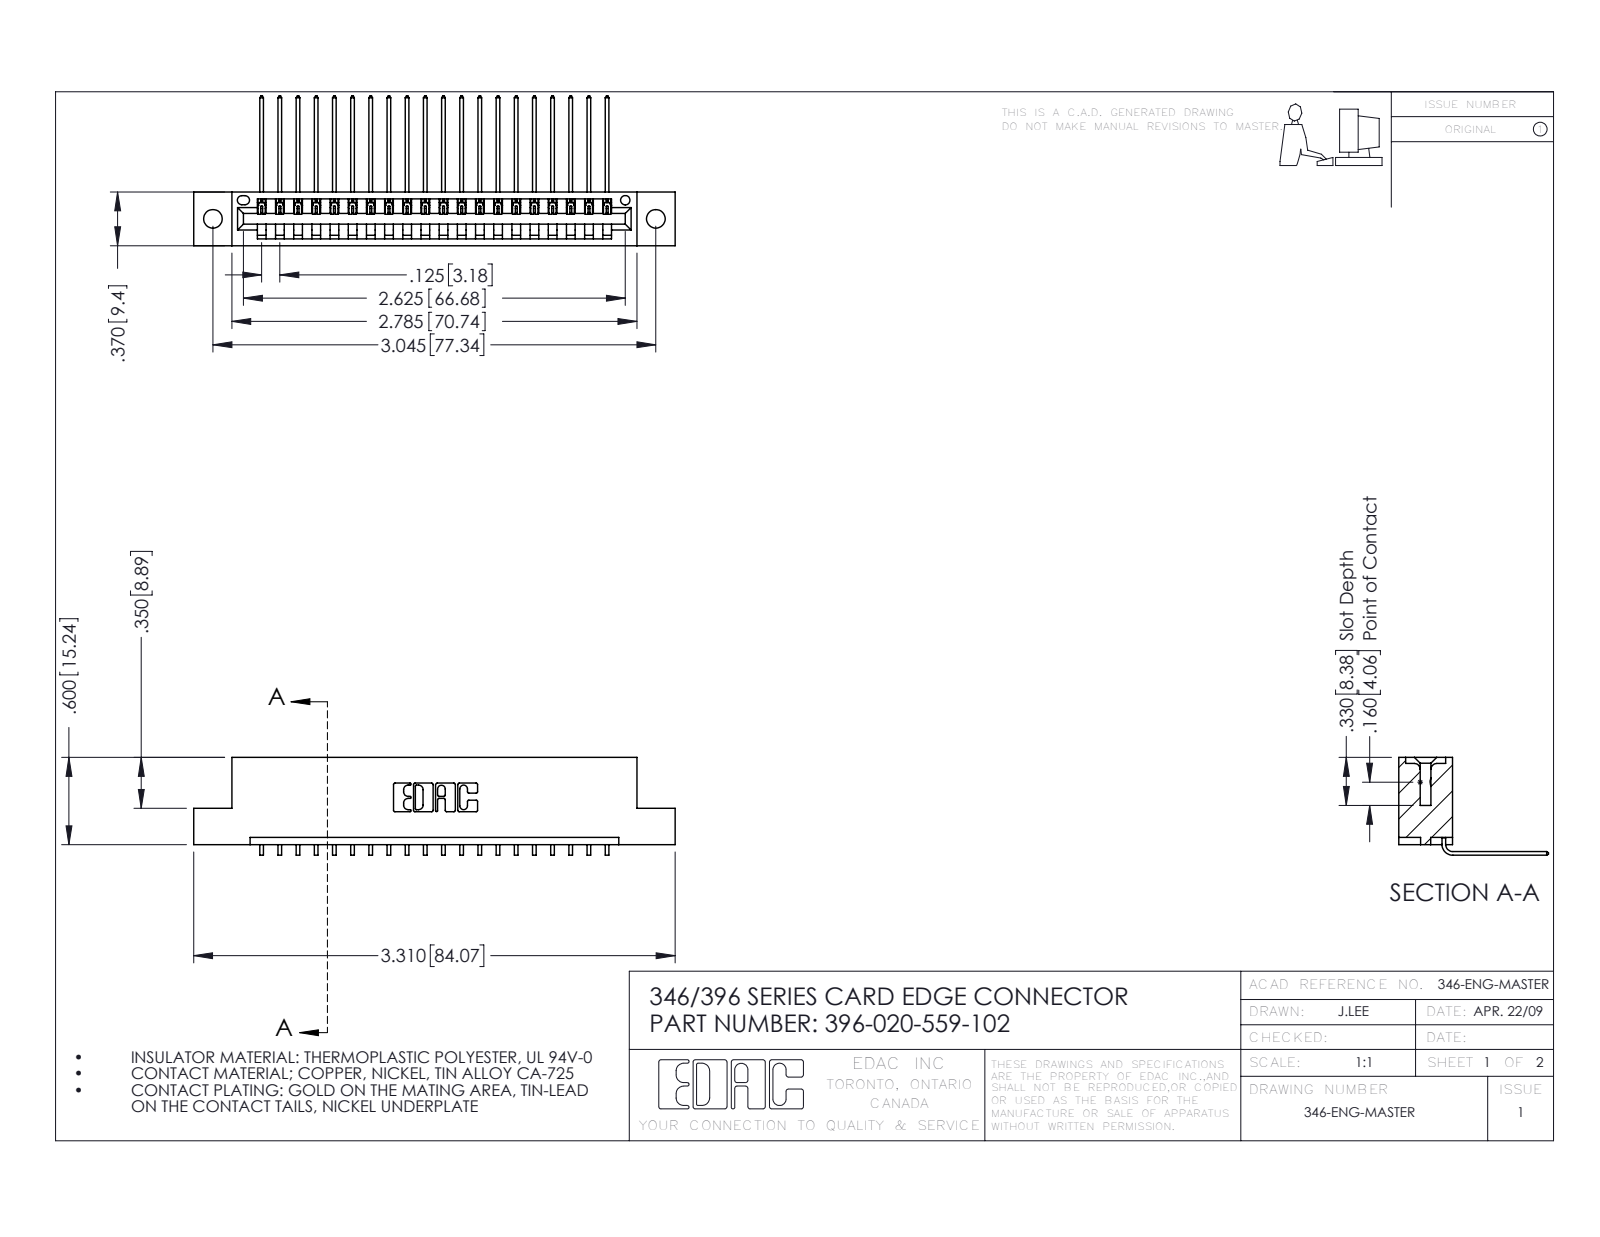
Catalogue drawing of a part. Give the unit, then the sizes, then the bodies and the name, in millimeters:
Units: millimetres
Overall size (bounding box): 84.1 × 26.2 × 17.1
Round holes (diameter × count): ⌀3.3 ×2, ⌀1.6 ×1
Partial cylindrical surfaces — rounded edges, fillets, slot ends (radius × count): R0.2 ×40, R0.3 ×22, R0.2 ×6, R0.8 ×6, R0.7 ×3, R0.8 ×2, R1 ×2, R0.4 ×1
Main face-to-face distances: 1.2, 8.2, 9.4, 6.4, 1.8, 0.6, 7.6, 3.8, 5.6, 2.5
Hole centre spacings: 6.2, 72.1, 77.3
Volume: 7 930 mm³ · Surface area: 9 794 mm²
Bodies: 21 solids, 1322 faces (916 planar, 406 cylindrical, 0 other)
Part name (STEP PRODUCT): 396-020-559-102; 345-292-001_558 559 Tail - 1; 346 Part_Flush Mounting Lugs - 0.128 Dia
STEP written by: SolidWorks 2016 (CONFIG_CONTROL_DESIGN)
